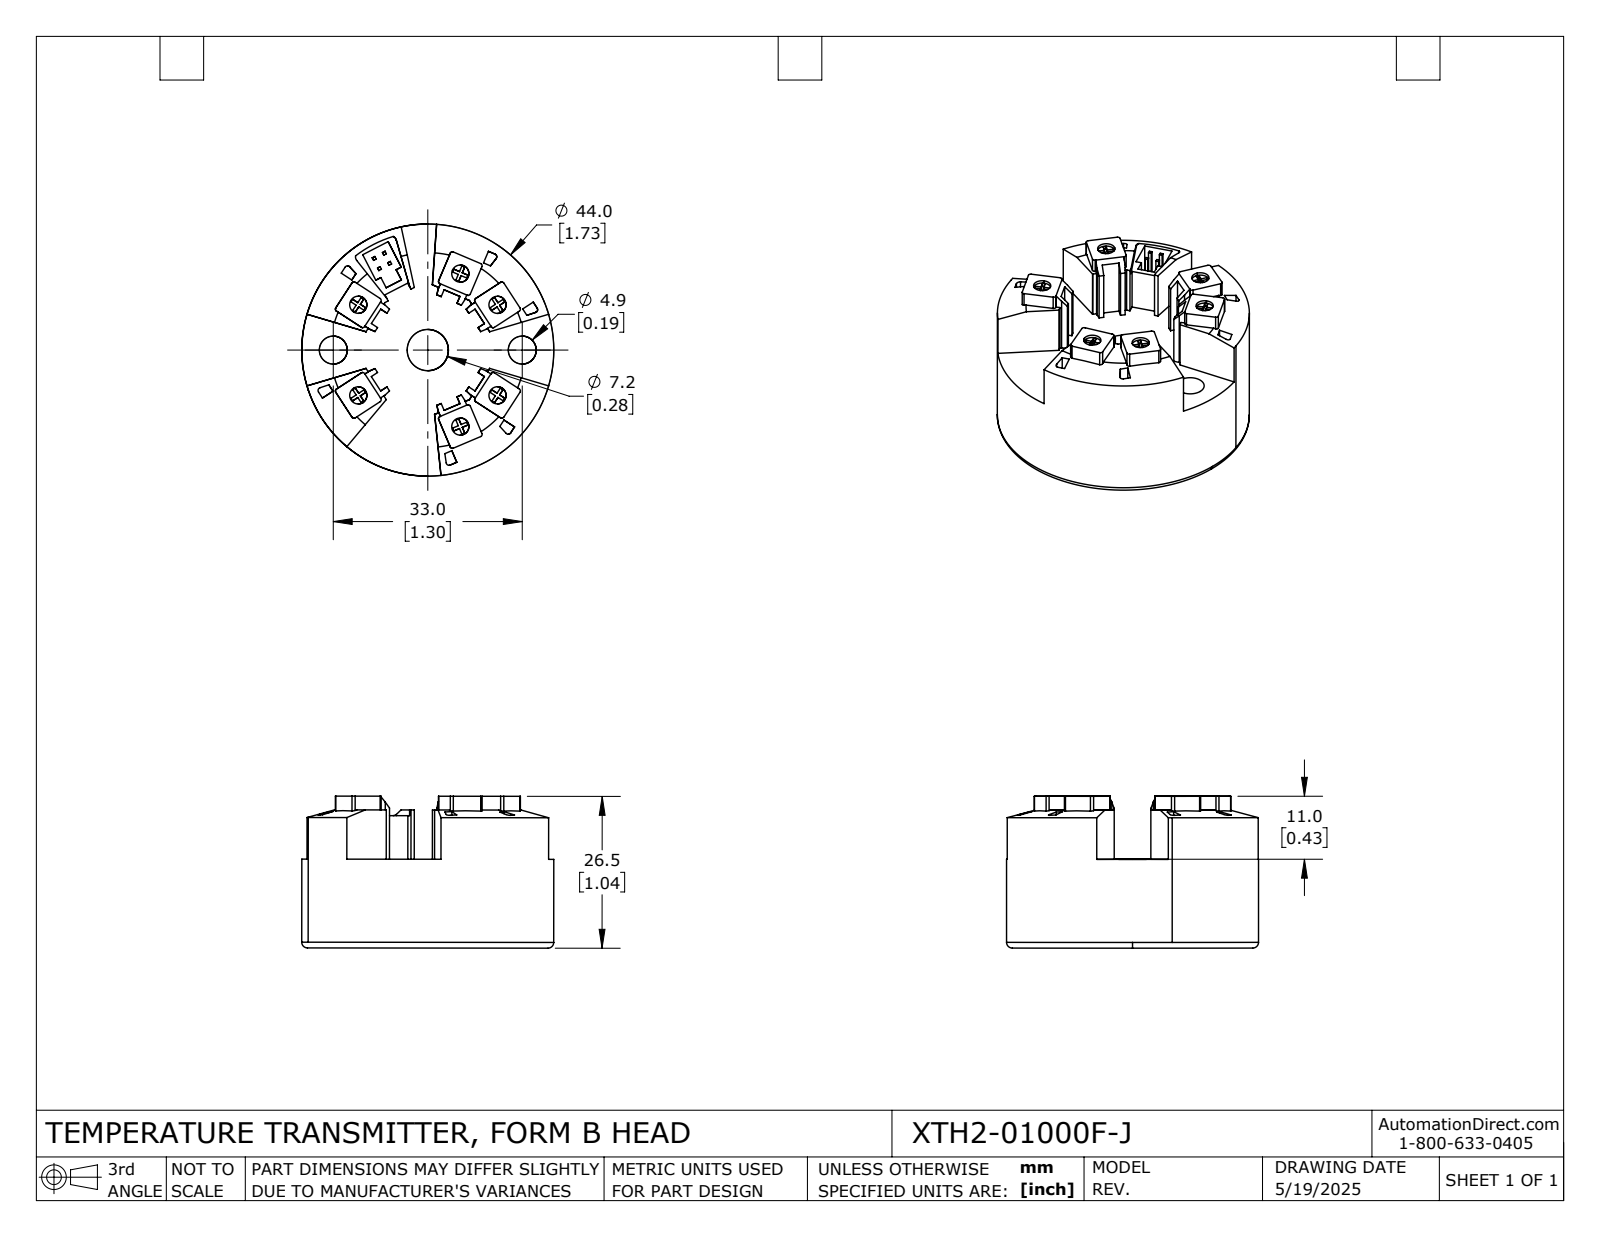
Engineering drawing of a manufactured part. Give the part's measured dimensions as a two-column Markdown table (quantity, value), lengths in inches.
| quantity | value |
| --- | --- |
| part name | XTDH2-01000F-J |
| STEP written by | SolidWorks 2024 (AUTOMOTIVE_DESIGN) |
| units | inches |
| bodies | 1 solid, 341 faces (281 planar, 52 cylindrical, 8 other) |
| overall size | 1.733 × 1.732 × 1.045 |
| volume | 1.748 in³ |
| surface area | 13.46 in² |
| round holes (diameter × count) | 0.118 × 6, 0.193 × 2, 0.283 × 1 |
| round bosses / shafts (diameter × count) | 1.732 × 1 |
| partial cylindrical surfaces (radius × count) | 0.016 × 24, 0.02 × 6, 0.039 × 2 |
| main face-to-face distances | 0.61, 1.043, 0.433, 0.059, 0.177, 0.039, 0.02, 0.118, 0.949, 0.339 |
| hole center spacings | 0.571, 0.333, 0.355, 0.356, 0.65, 0.677, 0.733, 0.875 |
